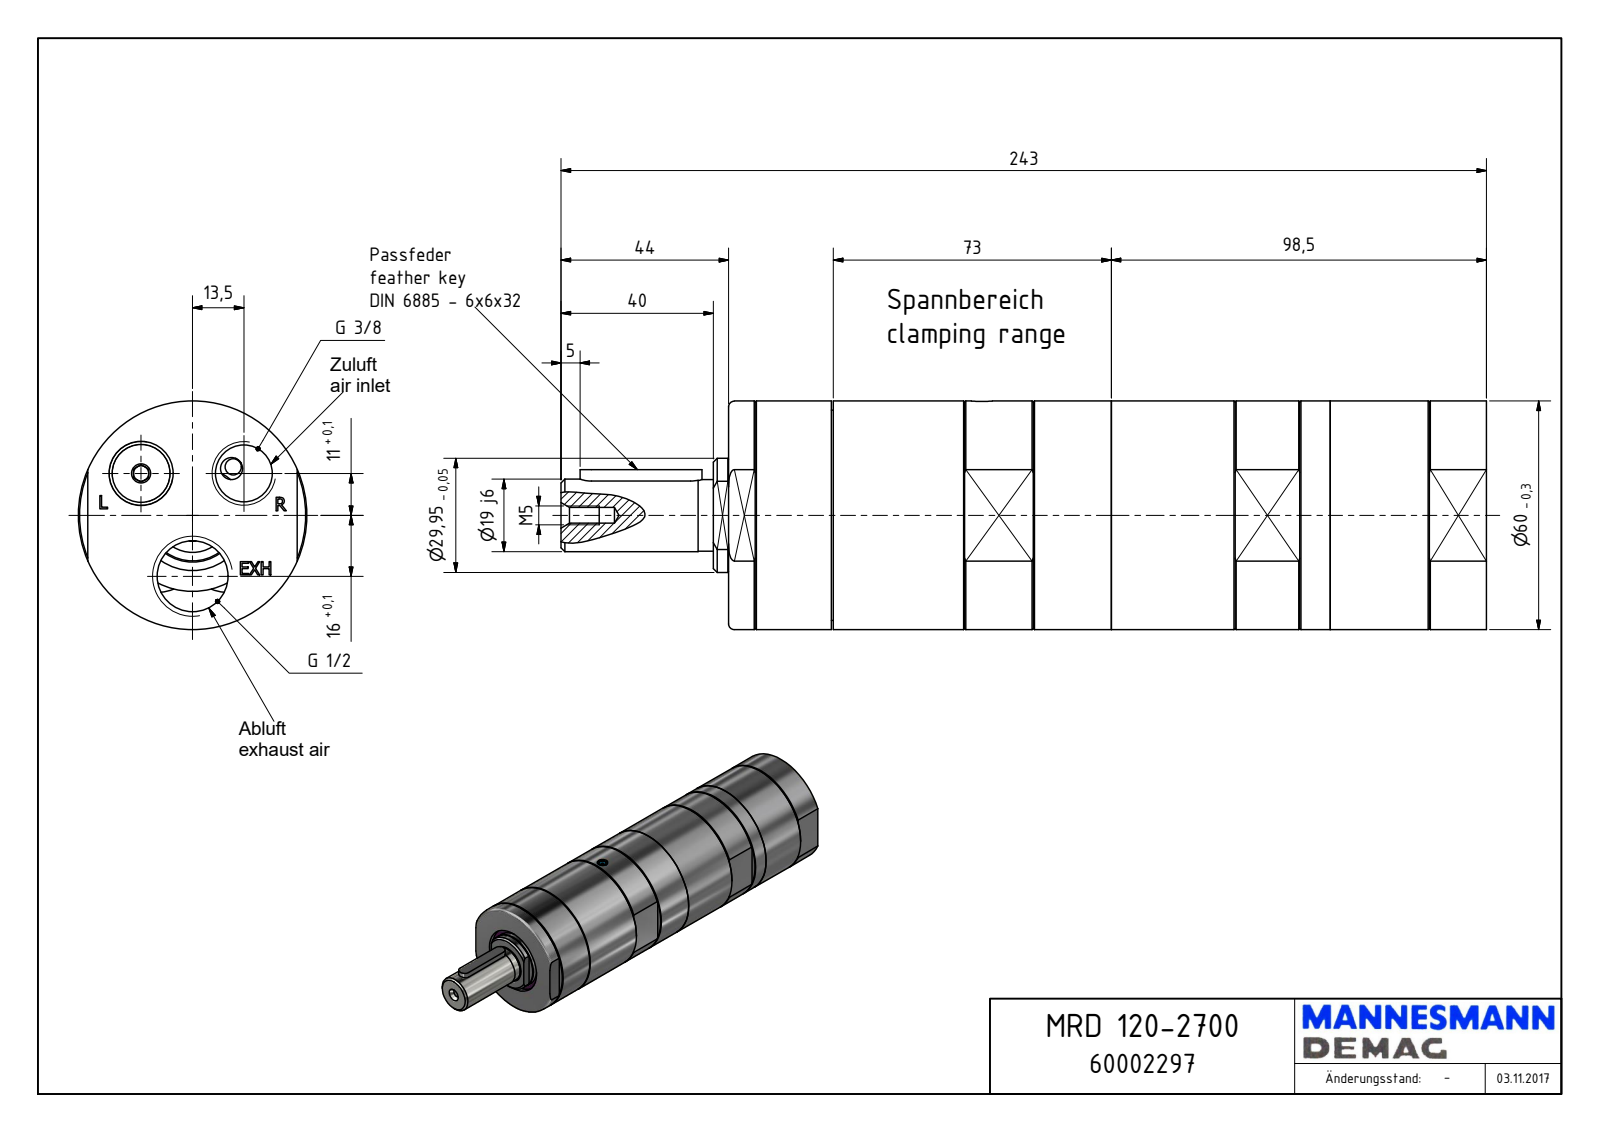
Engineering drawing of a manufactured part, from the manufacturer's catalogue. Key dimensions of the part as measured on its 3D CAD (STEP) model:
Part name (STEP PRODUCT): MRD 120-2700_60002297
STEP written by: Autodesk Inventor 2018 (AUTOMOTIVE_DESIGN)
Units: millimetres
Bodies: 1 solid, 222 faces (125 planar, 47 cylindrical, 50 other)
Overall size (bounding box): 243 × 60 × 60
Volume: 559 467 mm³ · Surface area: 53 314 mm²
Round holes (diameter × count): ⌀4 ×2, ⌀14.95 ×2, ⌀1.55 ×1, ⌀4.13 ×1, ⌀5.5 ×1, ⌀18.63 ×1, ⌀35 ×1, ⌀53.38 ×1, ⌀55.38 ×1
Round bosses / shafts (diameter × count): ⌀60 ×1, ⌀55.18 ×1, ⌀53.18 ×1, ⌀29.95 ×1, ⌀19 ×1, ⌀18.8 ×1, ⌀5 ×1, ⌀3.6 ×1
Partial cylindrical surfaces — rounded edges, fillets, slot ends (radius × count): R3 ×2, R7.5 ×2, R8.5 ×1, R19.21 ×1, R23.5 ×1, R26.99 ×1
Main face-to-face distances: 199, 55, 182.04, 16.96, 186, 3.96, 13, 27.5, 154.54, 158.5
Hole centre spacings: 17.41, 30.19, 16, 27
